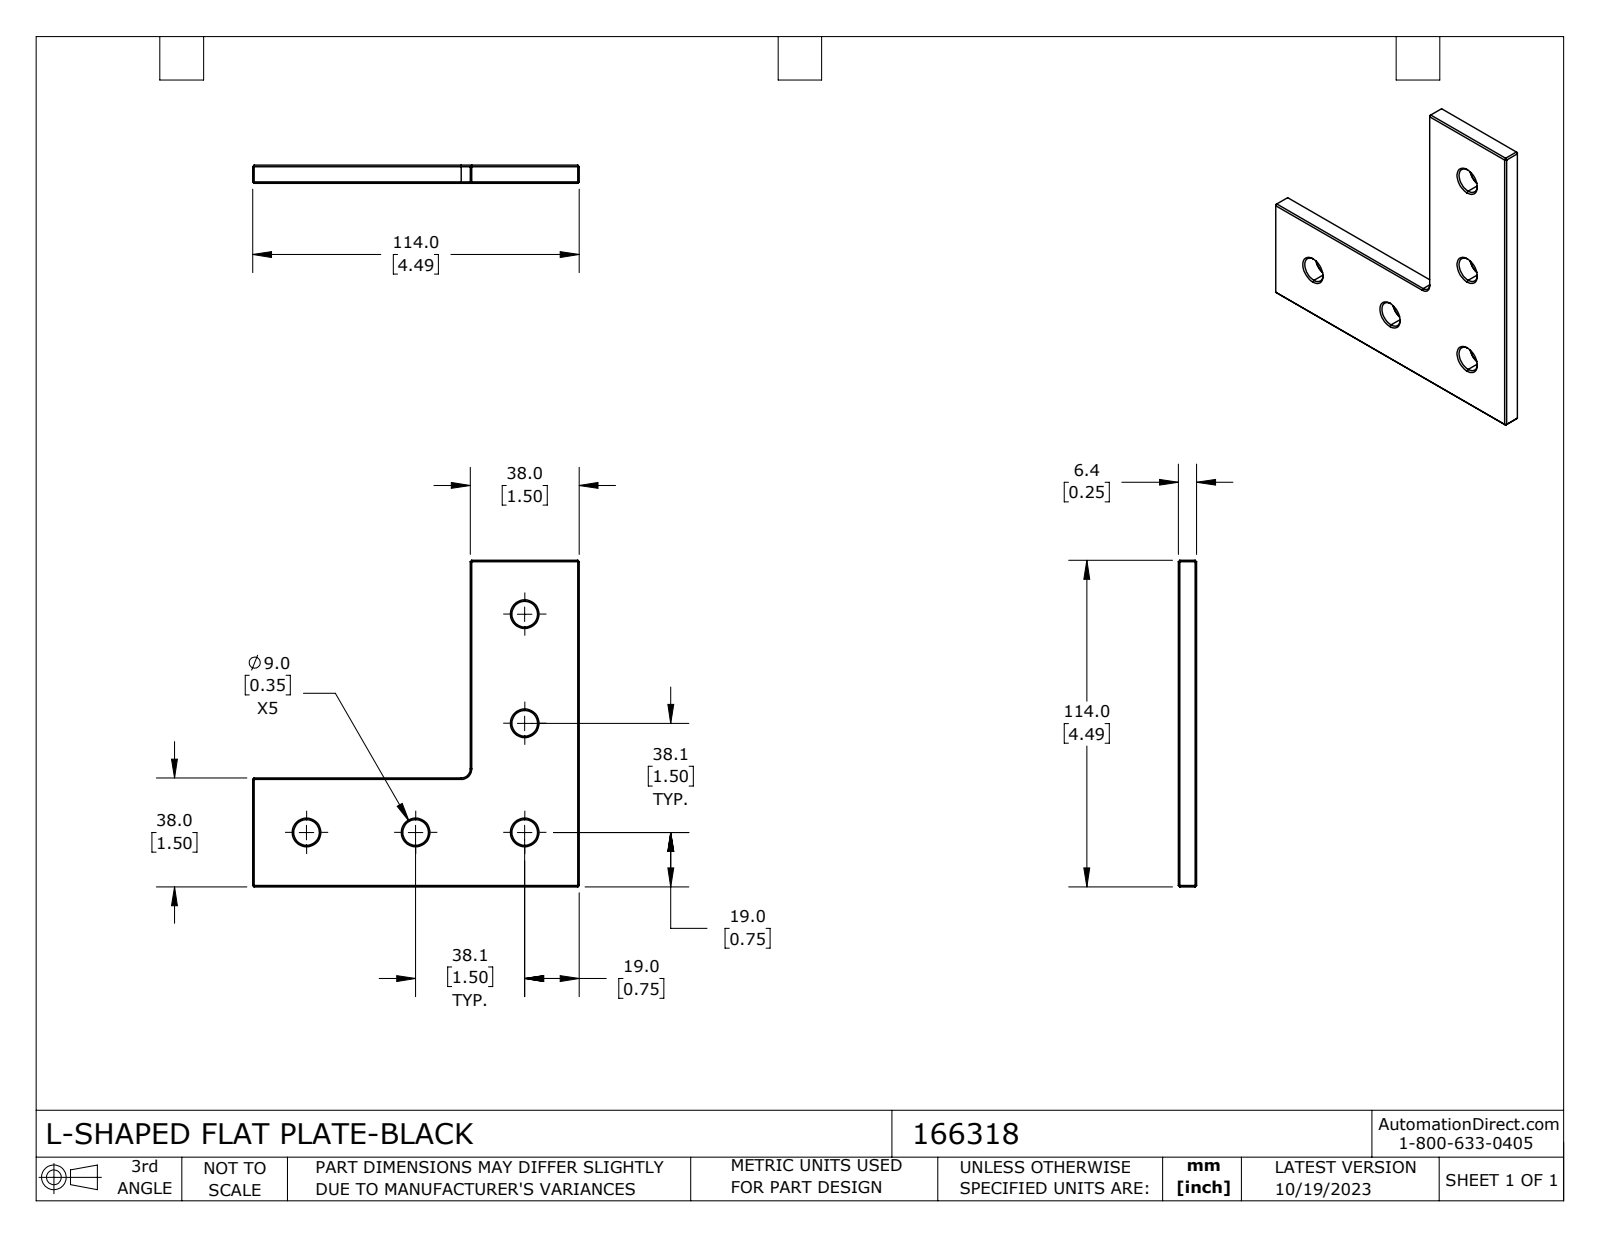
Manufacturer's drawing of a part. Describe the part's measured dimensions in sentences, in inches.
The part is named "166318". Its 3-D file was written by "SolidWorks 2023 (CONFIG_CONTROL_DESIGN)". It is 1 solid with 68 faces: 35 planar, 11 cylindrical and 22 other. Overall it measures 4.488 by 4.488 by 0.25 inches. Its volume is 2.666 cubic inches and its surface area 26.72 square inches. Round holes: 5 of diameter 0.354. Partial cylindrical surfaces (rounded edges, fillets, slot ends): 1 of radius 0.125. The main face-to-face distances are 0.25, 1.496, 2.992, 4.488, 1.207, 2.115, 3.322, 4.203, 6.318, 5.278. The hole center spacings are 1.5, 3, 3.354, 2.121, 4.243.
